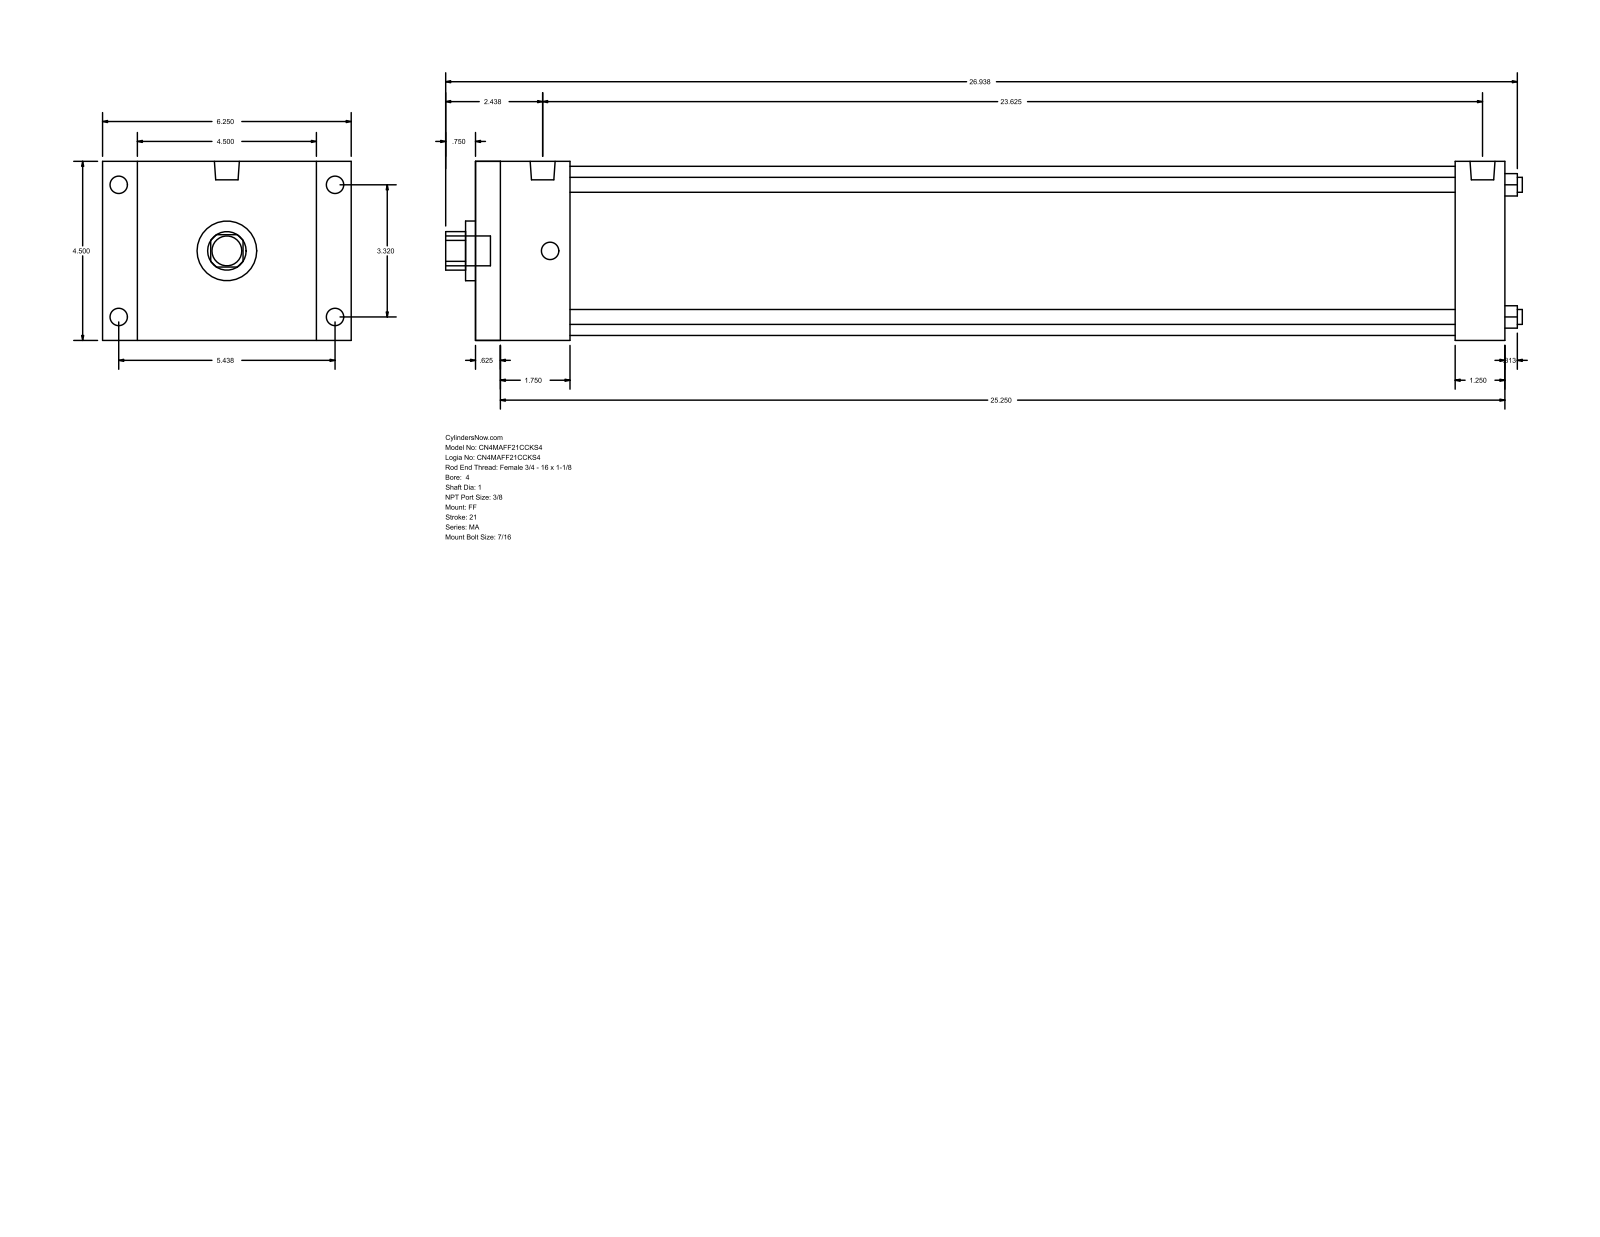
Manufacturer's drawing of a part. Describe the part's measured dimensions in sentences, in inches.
The part is named "MA_FF__0400_1". Its 3-D file was written by "GSSL Pune (CONFIG_CONTROL_DESIGN)". It is 0 solids with 92 faces: 64 planar, 28 cylindrical and 0 other. Overall it measures 27.063 by 6.25 by 4.5 inches. Round holes: 4 of diameter 0.375, 1 of diameter 1, 1 of diameter 1.5, 1 of diameter 4.25. Round bosses or shafts: 8 of diameter 0.437, 2 of diameter 0.627, 1 of diameter 0.75. Partial cylindrical surfaces (rounded edges, fillets, slot ends): 1 of radius 0.484. The main face-to-face distances are 4.5, 25.875, 0.625, 25.25, 0.875, 5.375, 24.625, 24, 1.25, 2.375. The hole center spacings are 2.347, 3.32, 4.695.
